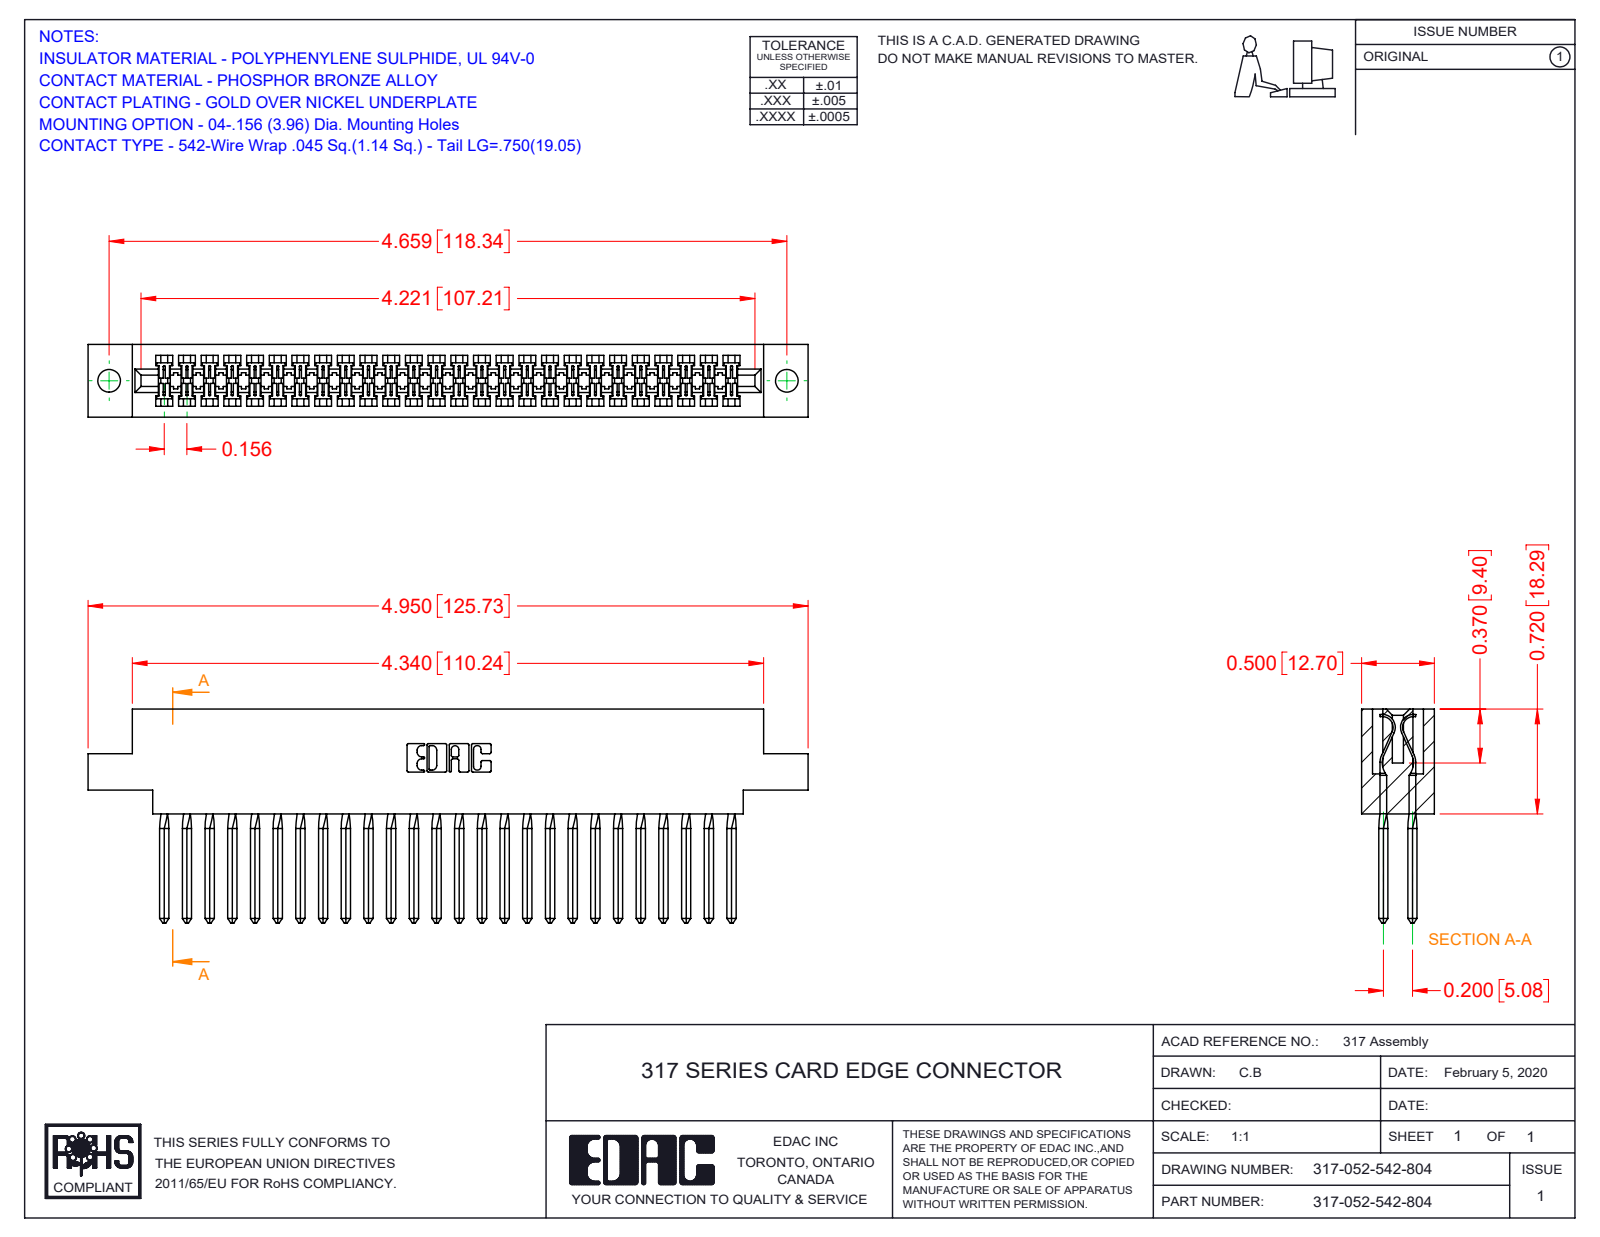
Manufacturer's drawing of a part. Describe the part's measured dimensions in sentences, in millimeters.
The part is named "317-290-003_542; 317-052-542-804; 317 Part_.156 Dia - TH". Its 3-D file was written by "SolidWorks 2016 (CONFIG_CONTROL_DESIGN)". It is 53 solids with 3066 faces: 2450 planar, 408 cylindrical and 208 other. Overall it measures 125.7 by 37.3 by 12.7 millimeters. Its volume is 19 990 cubic millimeters and its surface area 27 110 square millimeters. Round holes: 2 of diameter 4. Partial cylindrical surfaces (rounded edges, fillets, slot ends): 104 of radius 0.2, 22 of radius 0.3, 6 of radius 0.2, 6 of radius 0.8, 3 of radius 0.7, 2 of radius 1.9, 2 of radius 2.3, 2 of radius 2.5. The main face-to-face distances are 12.7, 1.9, 10.8, 8.9, 5.1, 2.8, 2.9, 1.2, 18.3, 3.5. The hole center spacings are 118.3.
